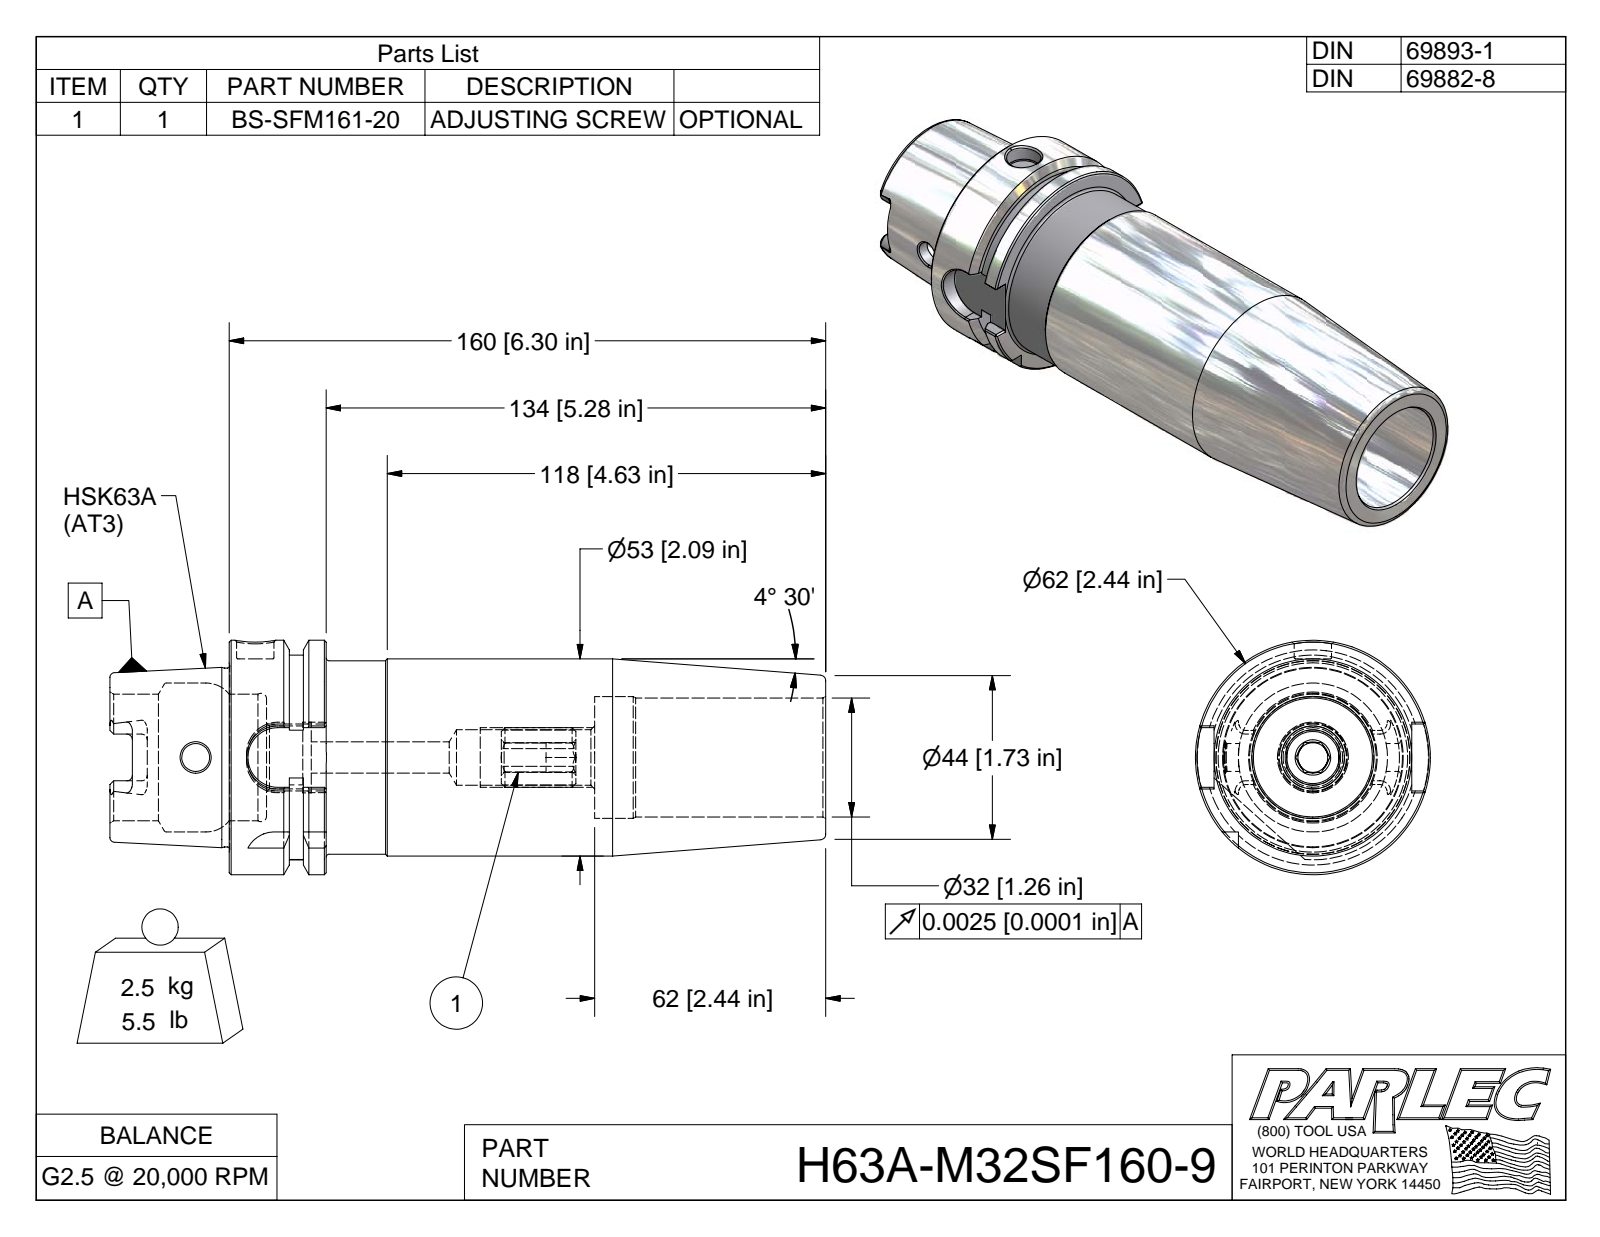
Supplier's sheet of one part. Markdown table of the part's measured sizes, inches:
| quantity | value |
| --- | --- |
| part name | H63A-M32SF160-9; H63A-M32SF160-9-1; BS-SFM161-20 |
| STEP written by | Autodesk Inventor 2009 (AUTOMOTIVE_DESIGN) |
| units | inches |
| bodies | 2 solids, 167 faces (65 planar, 37 cylindrical, 65 other) |
| overall size | 7.56 × 2.48 × 2.48 |
| volume | 18.26 in³ |
| surface area | 83.53 in² |
| round holes (diameter × count) | 0.295 × 1, 0.394 × 1, 0.666 × 1, 0.749 × 1, 1.258 × 1, 1.288 × 1, 1.339 × 1, 1.575 × 1 |
| round bosses / shafts (diameter × count) | 2.48 × 1, 2.087 × 1, 2.047 × 1, 1.891 × 1 |
| partial cylindrical surfaces (radius × count) | 0.059 × 6, 0.315 × 5, 0.113 × 4, 1.083 × 1 |
| main face-to-face distances | 1.024, 0.241, 0.389, 3.859, 2.835, 0.394, 0.63, 3.465, 6.3, 5.906 |
